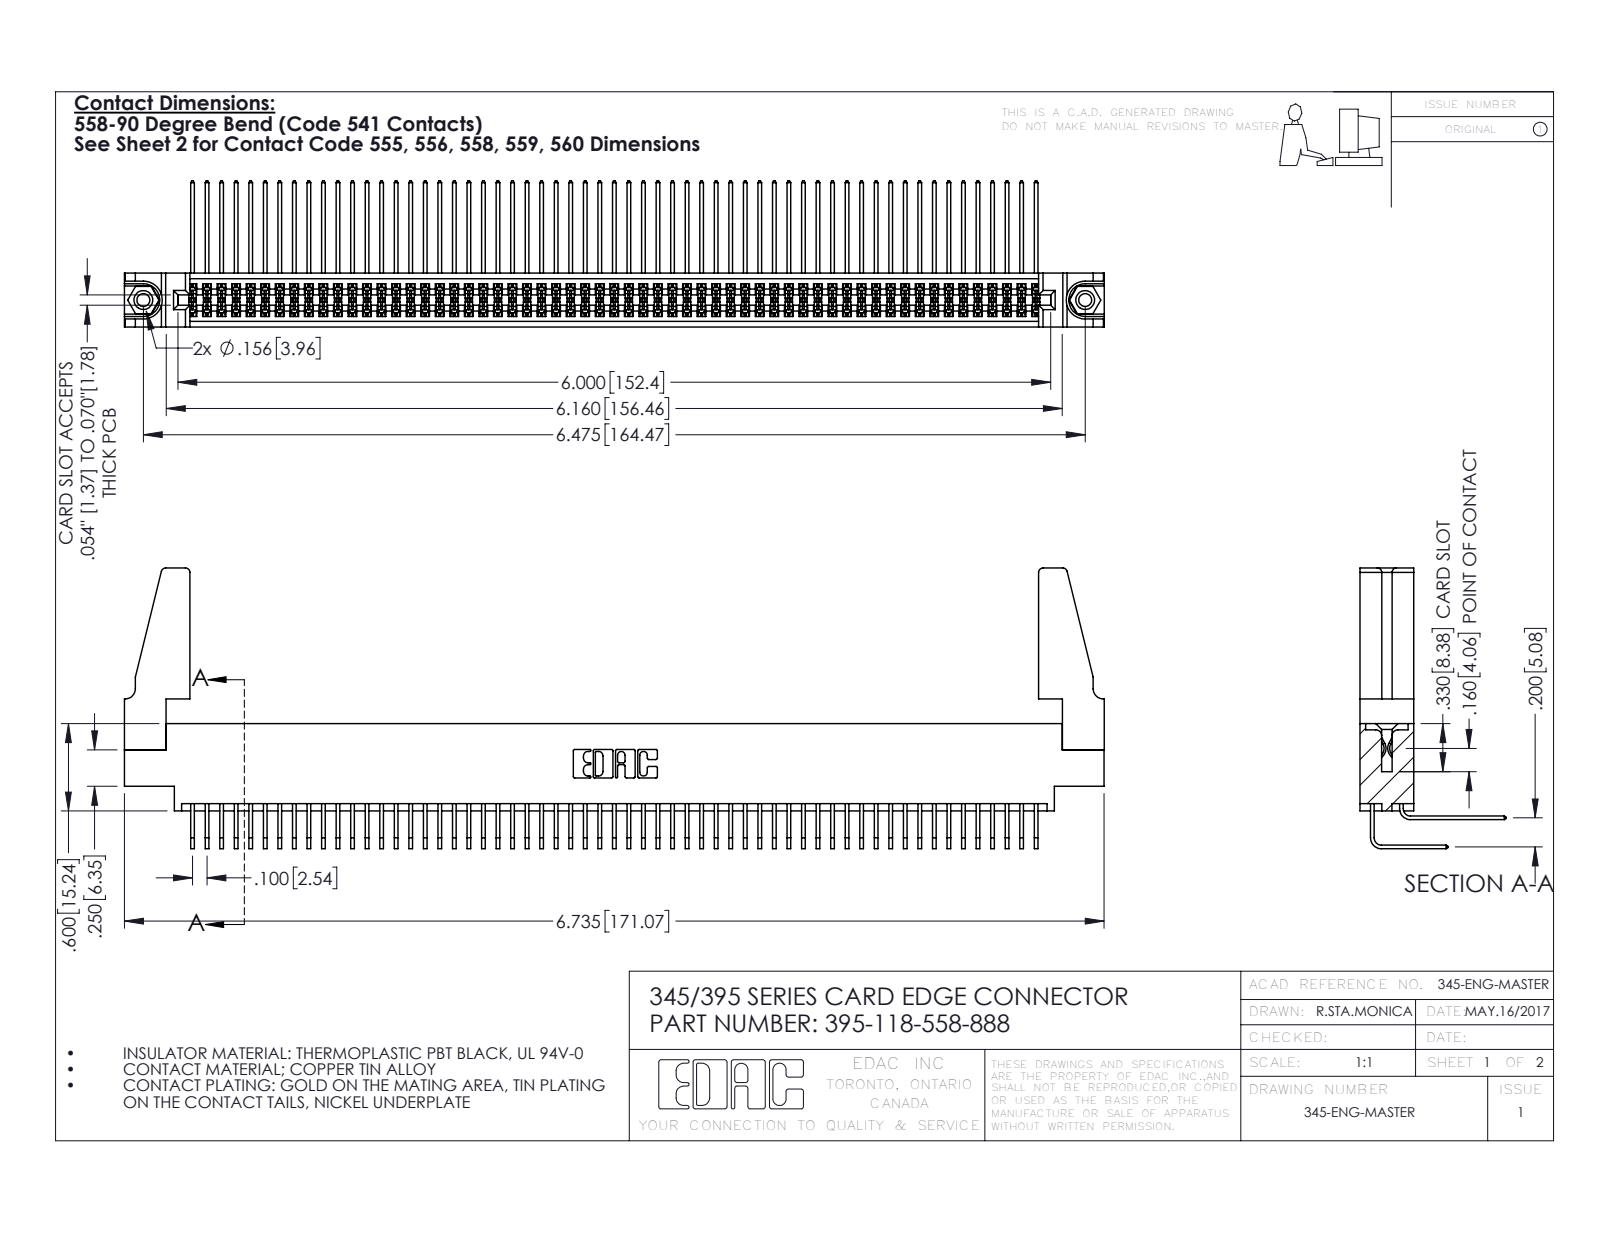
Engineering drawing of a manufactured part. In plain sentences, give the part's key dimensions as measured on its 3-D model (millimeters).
The part is named "345-220-078_345-220-088; 345-292-001_558 Tail - 2; 345-250-001_345-250-001-102; 345 Part_0.170 Offset - 0.156 Dia-TH (+2 more)". Its 3-D file was written by "SolidWorks 2016 (CONFIG_CONTROL_DESIGN)". It is 123 solids with 6390 faces: 4286 planar, 2088 cylindrical and 16 other. Overall it measures 171.1 by 49 by 25.5 millimeters. Its volume is 20 600 cubic millimeters and its surface area 32 430 square millimeters. Round holes: 2 of diameter 2.3, 2 of diameter 3.2, 2 of diameter 4, 1 of diameter 1.6. Round bosses or shafts: 2 of diameter 3.9. Partial cylindrical surfaces (rounded edges, fillets, slot ends): 178 of radius 0.2, 22 of radius 0.3, 8 of radius 0.8, 6 of radius 0.2, 6 of radius 0.8, 3 of radius 0.7, 2 of radius 0.4, 2 of radius 0.5. The main face-to-face distances are 1.8, 7.6, 5.1, 9.4, 2.5, 6.9, 0.6, 5.7, 4.4, 0.6. The hole center spacings are 6.9, 158.5, 164.5.
